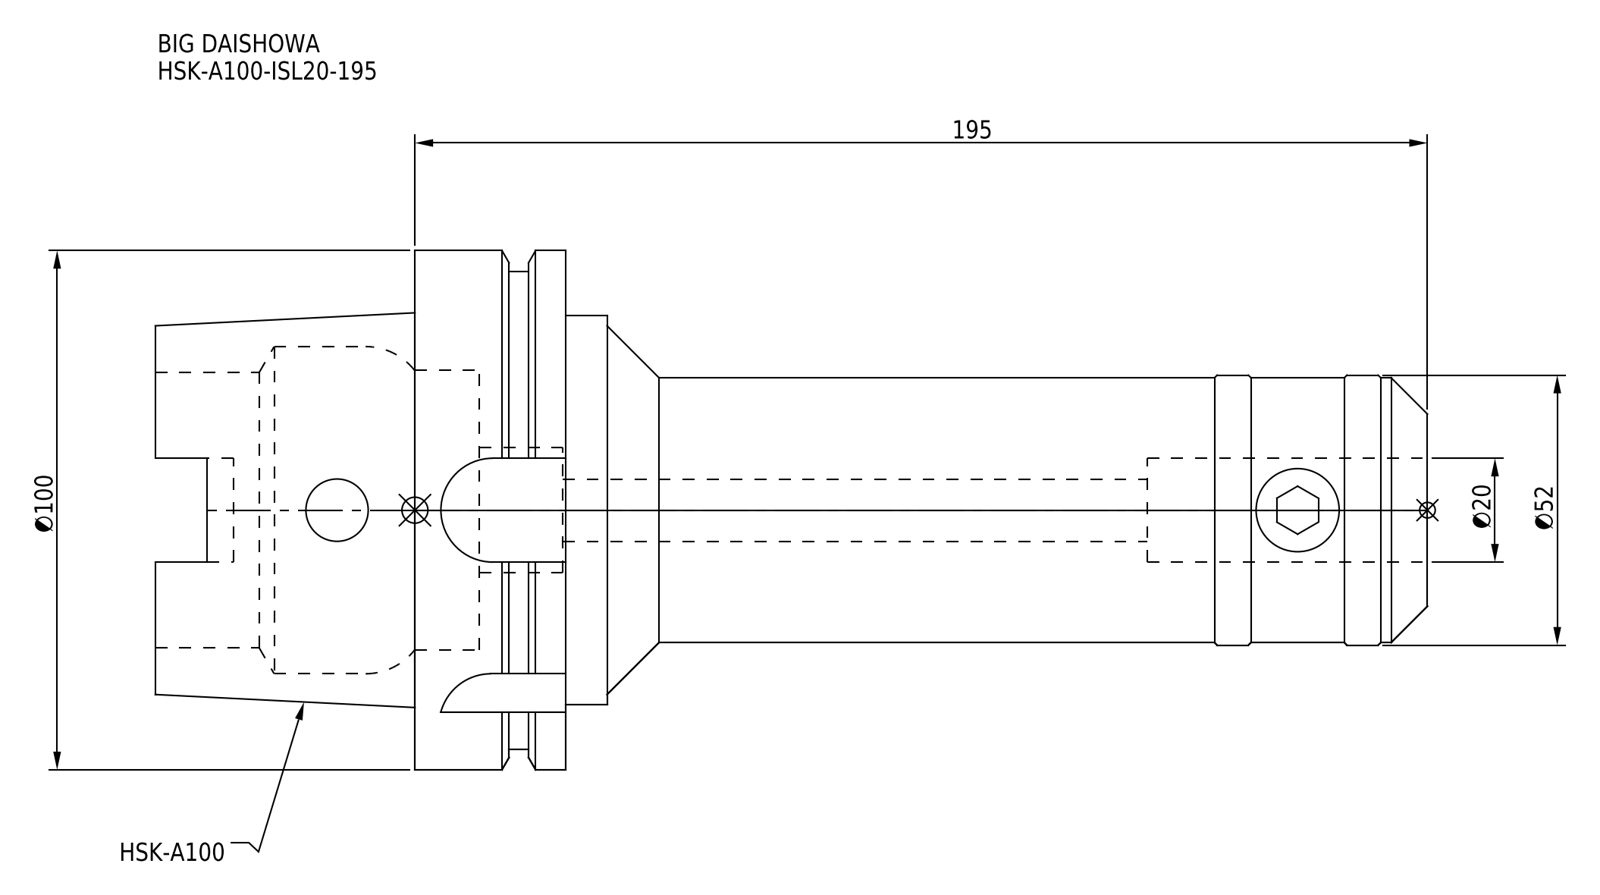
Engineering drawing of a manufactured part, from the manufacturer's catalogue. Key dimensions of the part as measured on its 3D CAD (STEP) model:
Part name (STEP PRODUCT): HSK-A100-ISL20-195
STEP written by: CREO PARAMETRIC BY PTC INC, 2016380 (AUTOMOTIVE_DESIGN)
Units: millimetres
Bodies: 1 solid, 96 faces (30 planar, 42 cylindrical, 24 other)
Overall size (bounding box): 245 × 100 × 100
Volume: 589 163 mm³ · Surface area: 83 596 mm²
Round holes (diameter × count): ⌀12 ×2, ⌀20 ×1, ⌀24 ×1, ⌀53 ×1, ⌀53.8 ×1, ⌀63 ×1
Round bosses / shafts (diameter × count): ⌀100 ×1, ⌀92 ×1, ⌀75 ×1, ⌀52 ×1, ⌀51 ×1
Partial cylindrical surfaces — rounded edges, fillets, slot ends (radius × count): R10 ×4
Main face-to-face distances: 29, 16.55, 12.45, 79, 62.45, 50, 166, 182.55, 195, 245
